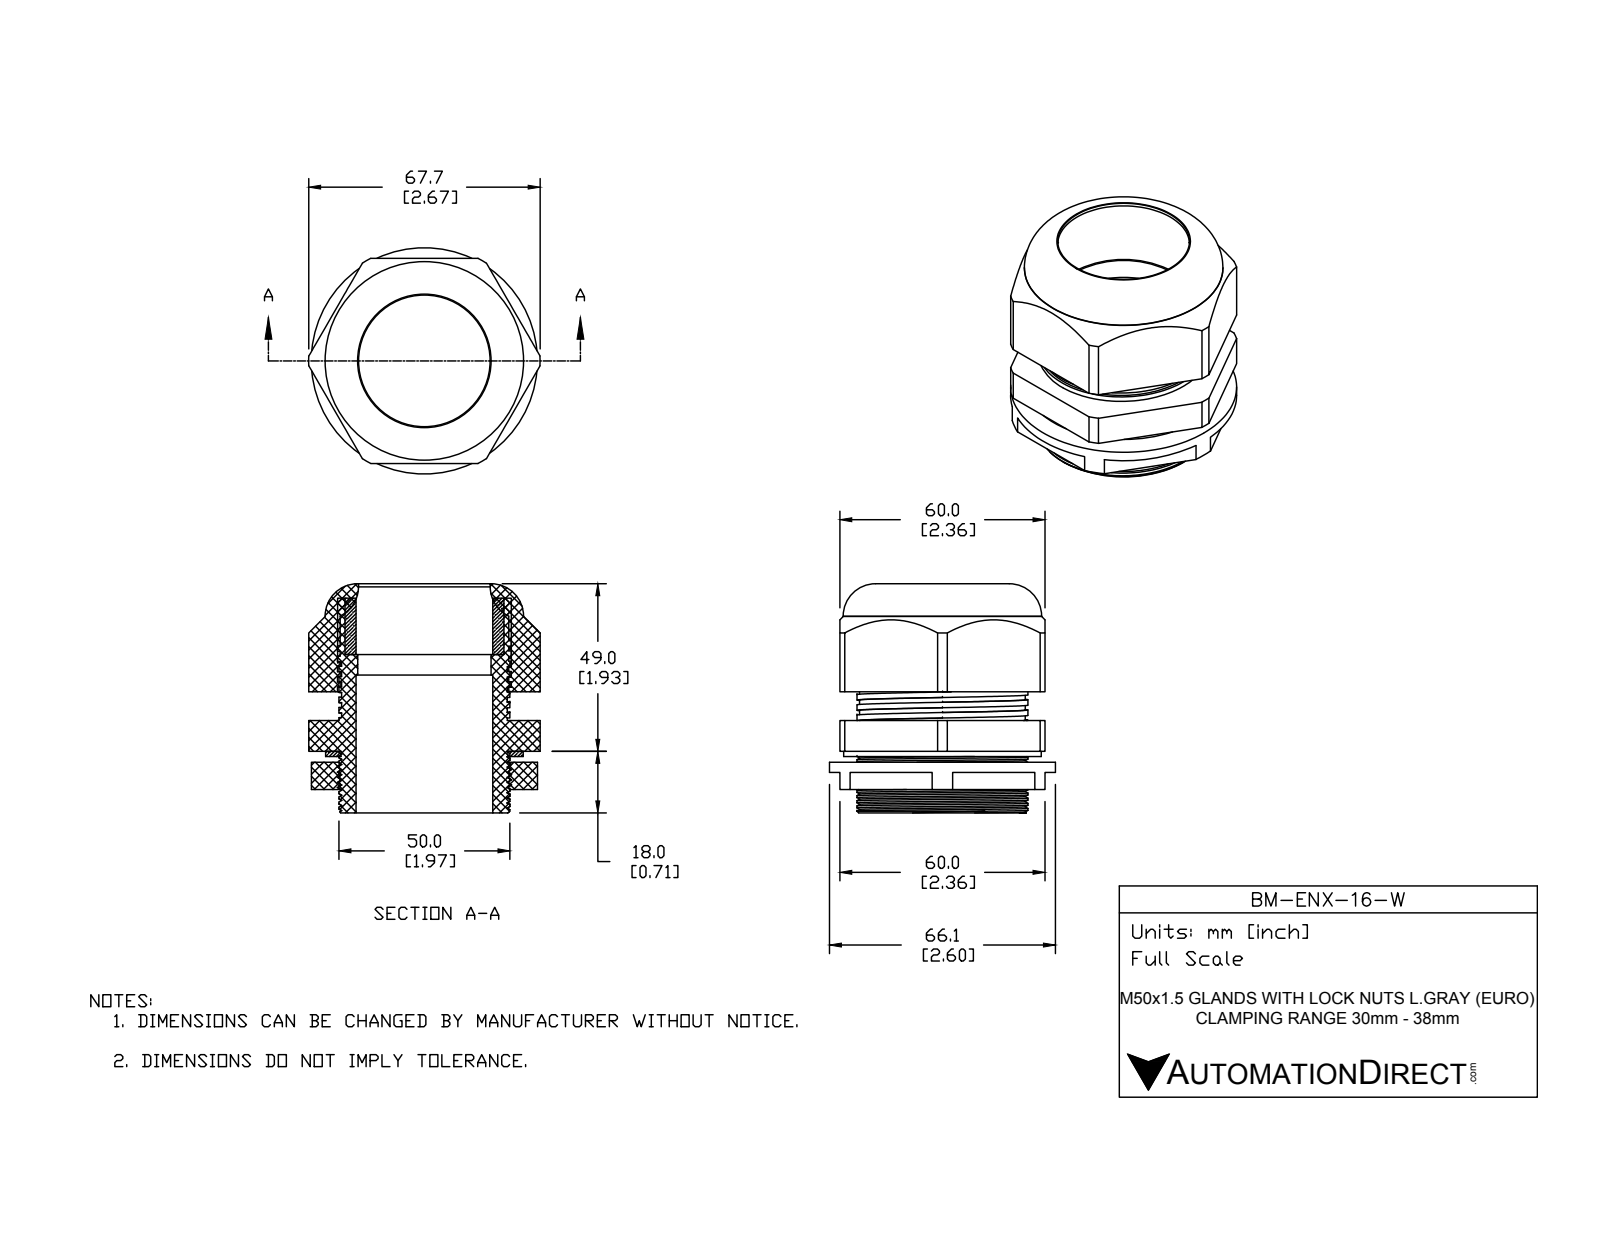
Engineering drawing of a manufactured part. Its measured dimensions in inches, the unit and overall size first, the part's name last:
Units: inches
Overall size (bounding box): 2.665 × 2.638 × 2.602
Round holes (diameter × count): ⌀1.516 ×1, ⌀1.535 ×1, ⌀1.575 ×1, ⌀1.831 ×1, ⌀1.921 ×1, ⌀1.942 ×1
Round bosses / shafts (diameter × count): ⌀2.602 ×1, ⌀2.286 ×1, ⌀2.276 ×1, ⌀2 ×1, ⌀1.969 ×1
Partial cylindrical surfaces — rounded edges, fillets, slot ends (radius × count): R1.333 ×1
Main face-to-face distances: 2.362, 0.125, 0.65, 1.823, 0.479, 0.354, 0.315, 0.44, 0.794, 1.125
Volume: 6.062 in³ · Surface area: 85.82 in²
Bodies: 5 solids, 256 faces (140 planar, 97 cylindrical, 19 other)
Part name (STEP PRODUCT): BM-ENX-16-W
STEP written by: SolidWorks 2015 (CONFIG_CONTROL_DESIGN)
